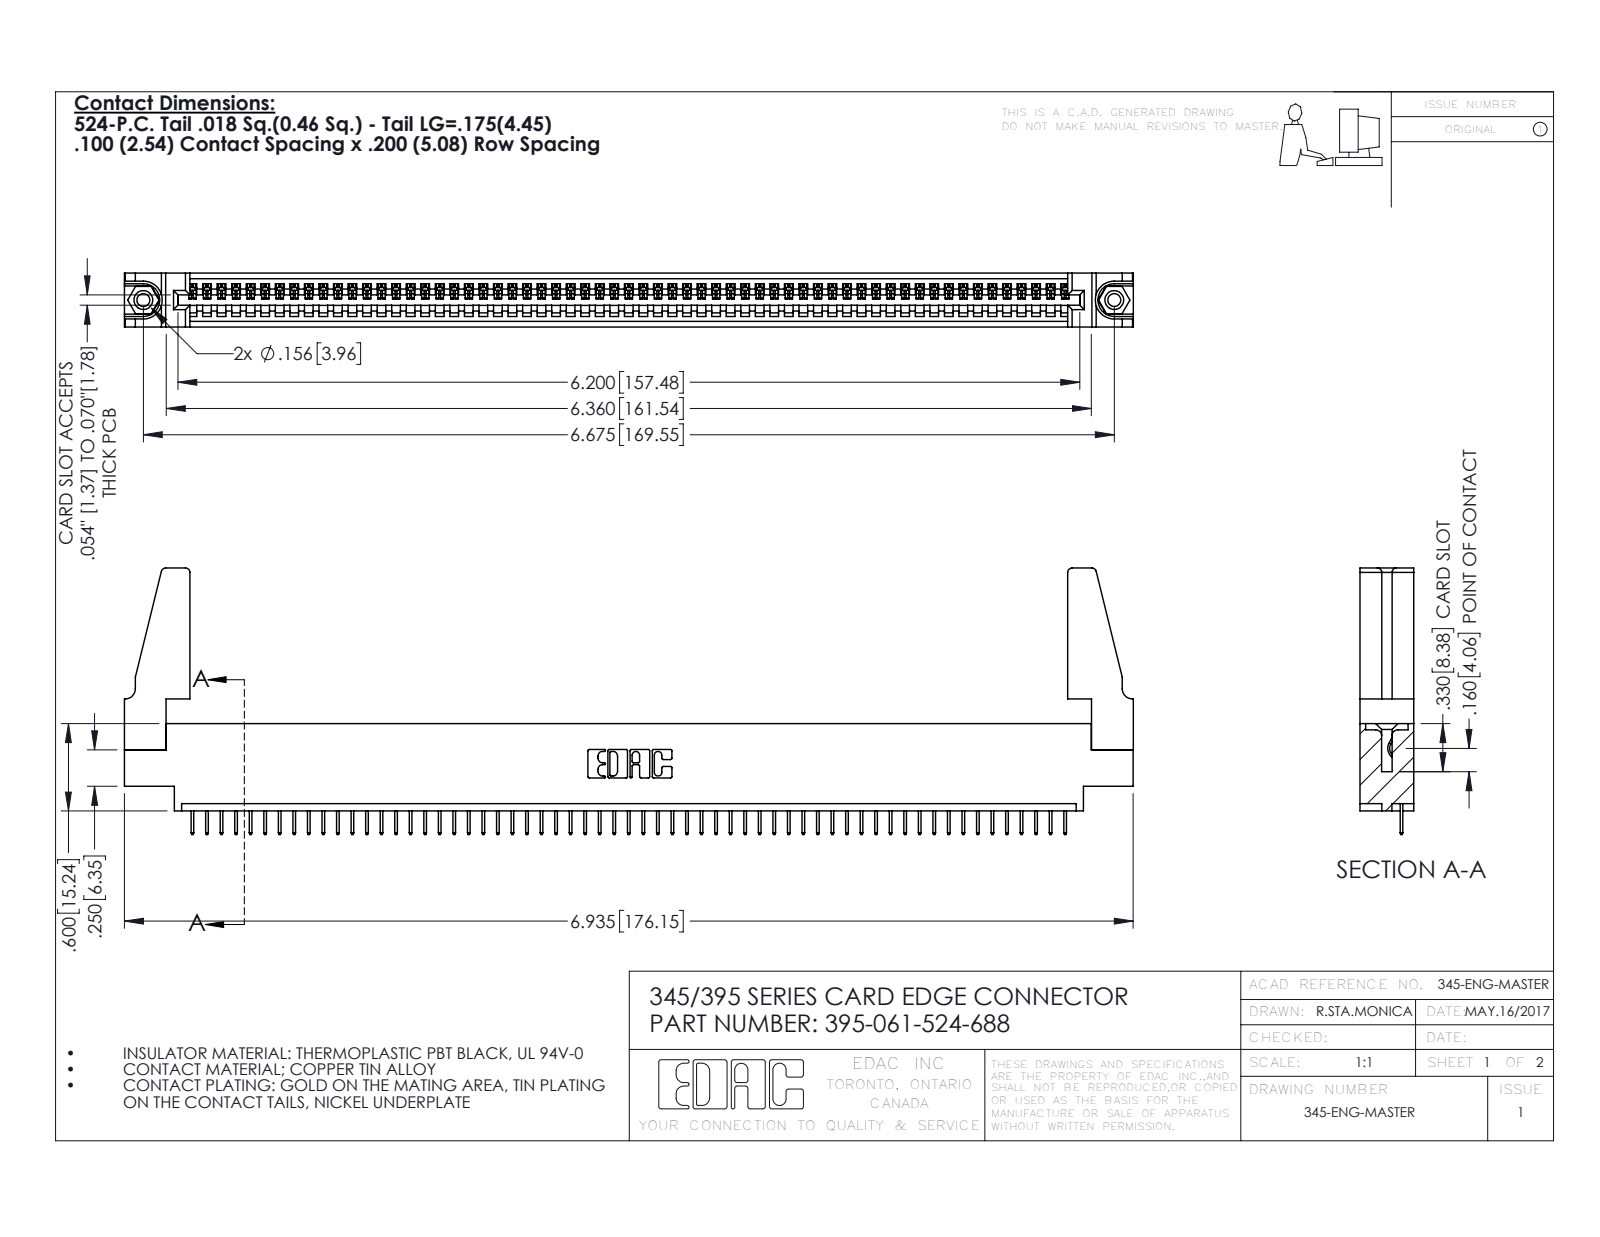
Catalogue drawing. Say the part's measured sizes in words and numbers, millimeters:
The part is named "345-220-078_345-220-088; 345-250-001_345-250-001-102; 345-292-001_345-293-124; 395-061-524-688 (+1 more)". Its 3-D file was written by "SolidWorks 2016 (CONFIG_CONTROL_DESIGN)". It is 66 solids with 4036 faces: 2962 planar, 1058 cylindrical and 16 other. Overall it measures 176.2 by 46.5 by 9.4 millimeters. Its volume is 19 780 cubic millimeters and its surface area 24 720 square millimeters. Round holes: 2 of diameter 2.3, 2 of diameter 3.2, 2 of diameter 4, 1 of diameter 1.6. Round bosses or shafts: 2 of diameter 3.9. Partial cylindrical surfaces (rounded edges, fillets, slot ends): 122 of radius 0.2, 22 of radius 0.3, 8 of radius 0.8, 6 of radius 0.2, 6 of radius 0.8, 3 of radius 0.7, 2 of radius 0.8, 2 of radius 1. The main face-to-face distances are 1.8, 9.4, 7.6, 2.5, 6.9, 0.6, 5.1, 5.7, 1.8, 4.4. The hole center spacings are 6.9, 163.6, 169.5.
